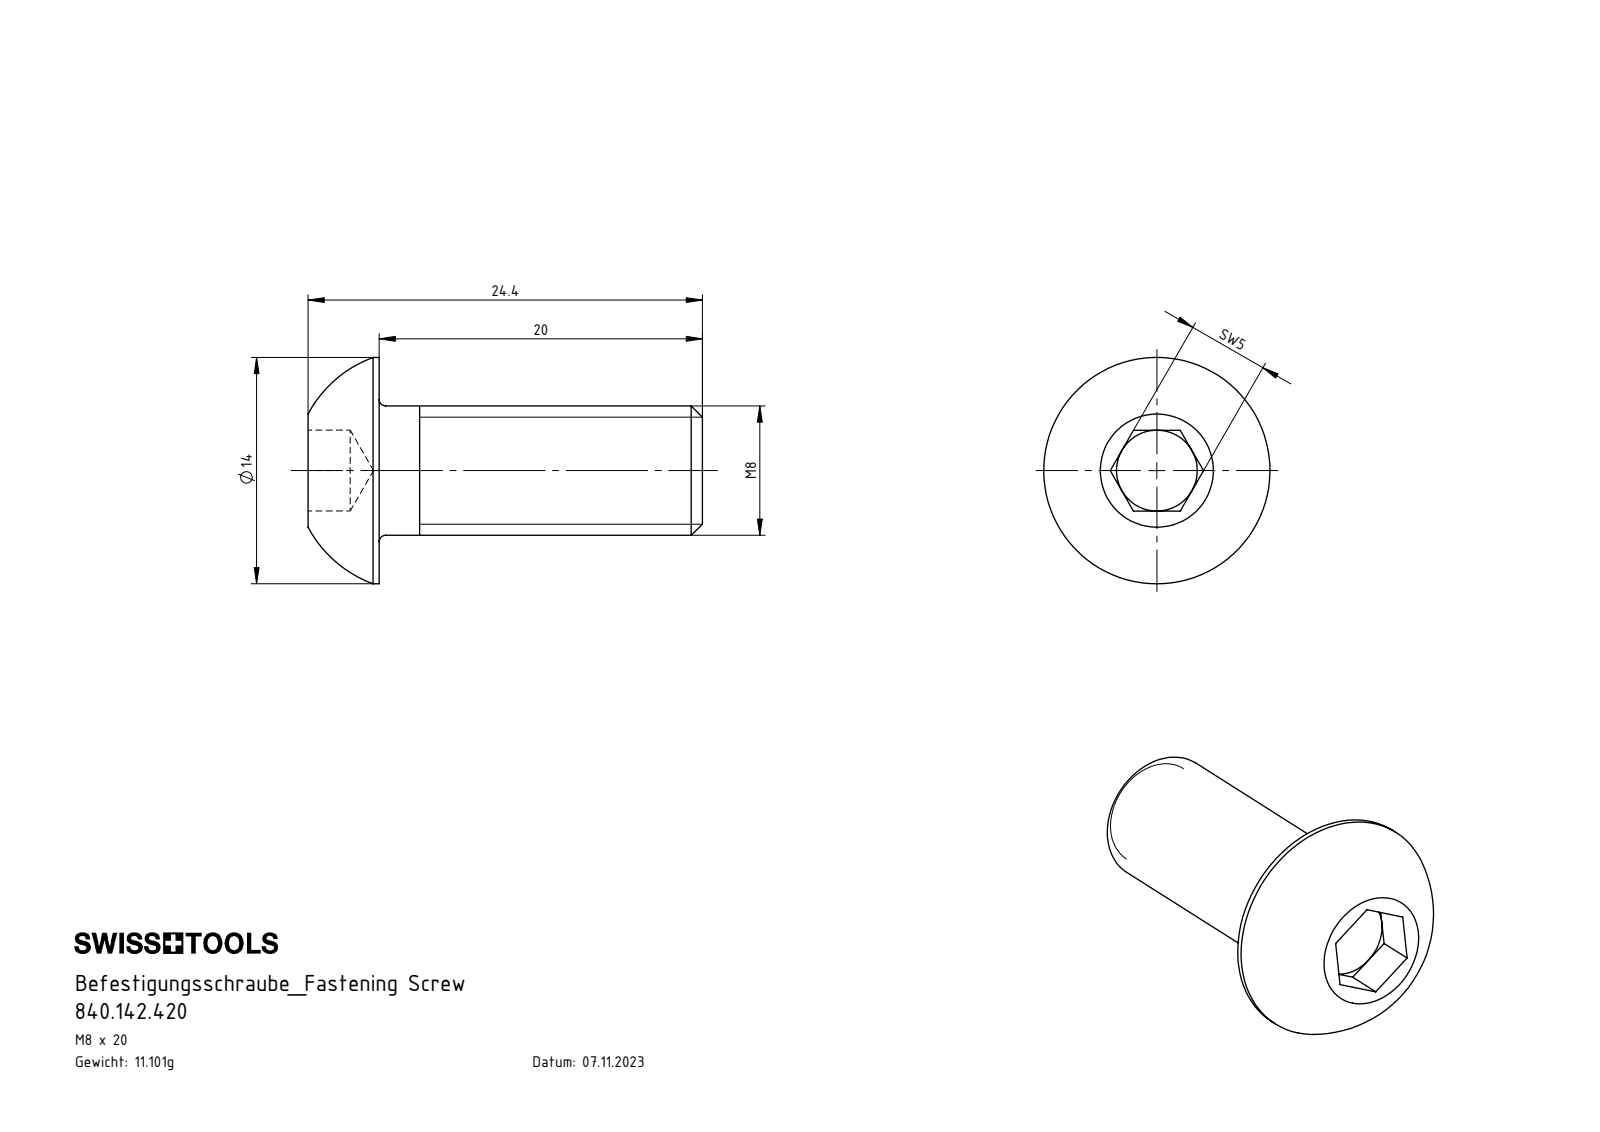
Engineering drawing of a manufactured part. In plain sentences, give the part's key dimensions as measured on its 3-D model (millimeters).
The part is named "840.142.420". Its 3-D file was written by "SolidWorks 2022 (AUTOMOTIVE_DESIGN)". It is 1 solid with 27 faces: 15 planar, 4 cylindrical and 8 other. Overall it measures 24.4 by 14 by 14 millimeters. Its volume is 1 414 cubic millimeters and its surface area 933 square millimeters. Round bosses or shafts: 1 of diameter 14, 1 of diameter 8. The main face-to-face distances are 20, 5, 4.4, 24.4, 2.6, 1.8, 21.8.
